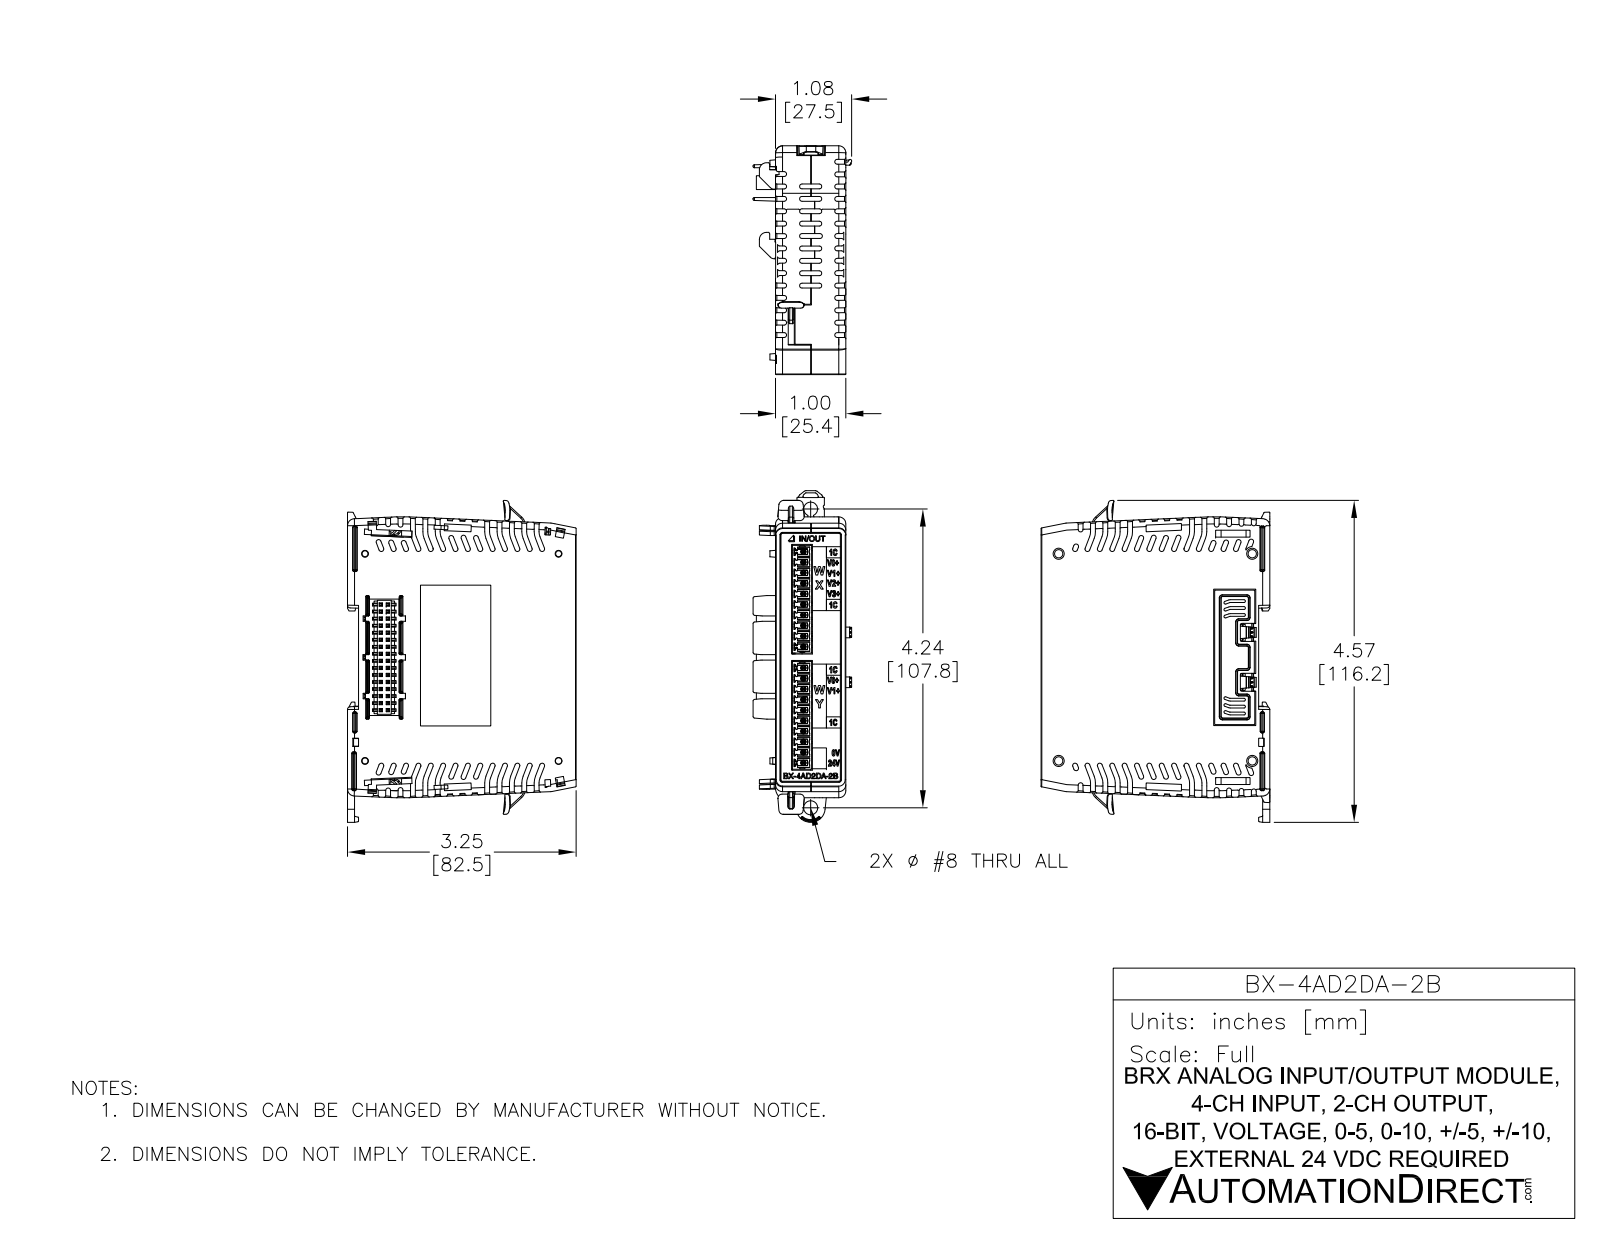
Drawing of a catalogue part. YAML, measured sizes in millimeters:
part_name: "BX-4AD2DA-2B"
step_written_by: "SolidWorks 2017 (AUTOMOTIVE_DESIGN)"
units: millimeters
bodies: {solids: 11, faces: 4629, planar: 3304, cylindrical: 627, other: 698}
overall_size: [116.5, 82.6, 35.6]
volume: 155000
surface_area: 57430
round_holes:
  - {diameter: 0.4, count: 8}
  - {diameter: 0.4, count: 2}
  - {diameter: 3, count: 2}
  - {diameter: 3, count: 2}
  - {diameter: 5.1, count: 1}
round_bosses_or_shafts:
  - {diameter: 2.8, count: 2}
  - {diameter: 1.5, count: 2}
  - {diameter: 1.8, count: 1}
partial_cylinders:
  - {radius: 0.5, count: 109}
  - {radius: 0.2, count: 103}
  - {radius: 0.1, count: 48}
  - {radius: 1.6, count: 20}
  - {radius: 0.3, count: 16}
  - {radius: 0.4, count: 16}
  - {radius: 0.3, count: 14}
  - {radius: 0.2, count: 12}
face_to_face_distances: [25.4, 21.2, 4.2, 77.5, 5.3, 15.9, 20.1, 52.1, 3.8, 25.1]
hole_center_spacings: [3.8, 7.6, 11.4, 15.2, 19.1, 41.9, 22.9, 38.1]
